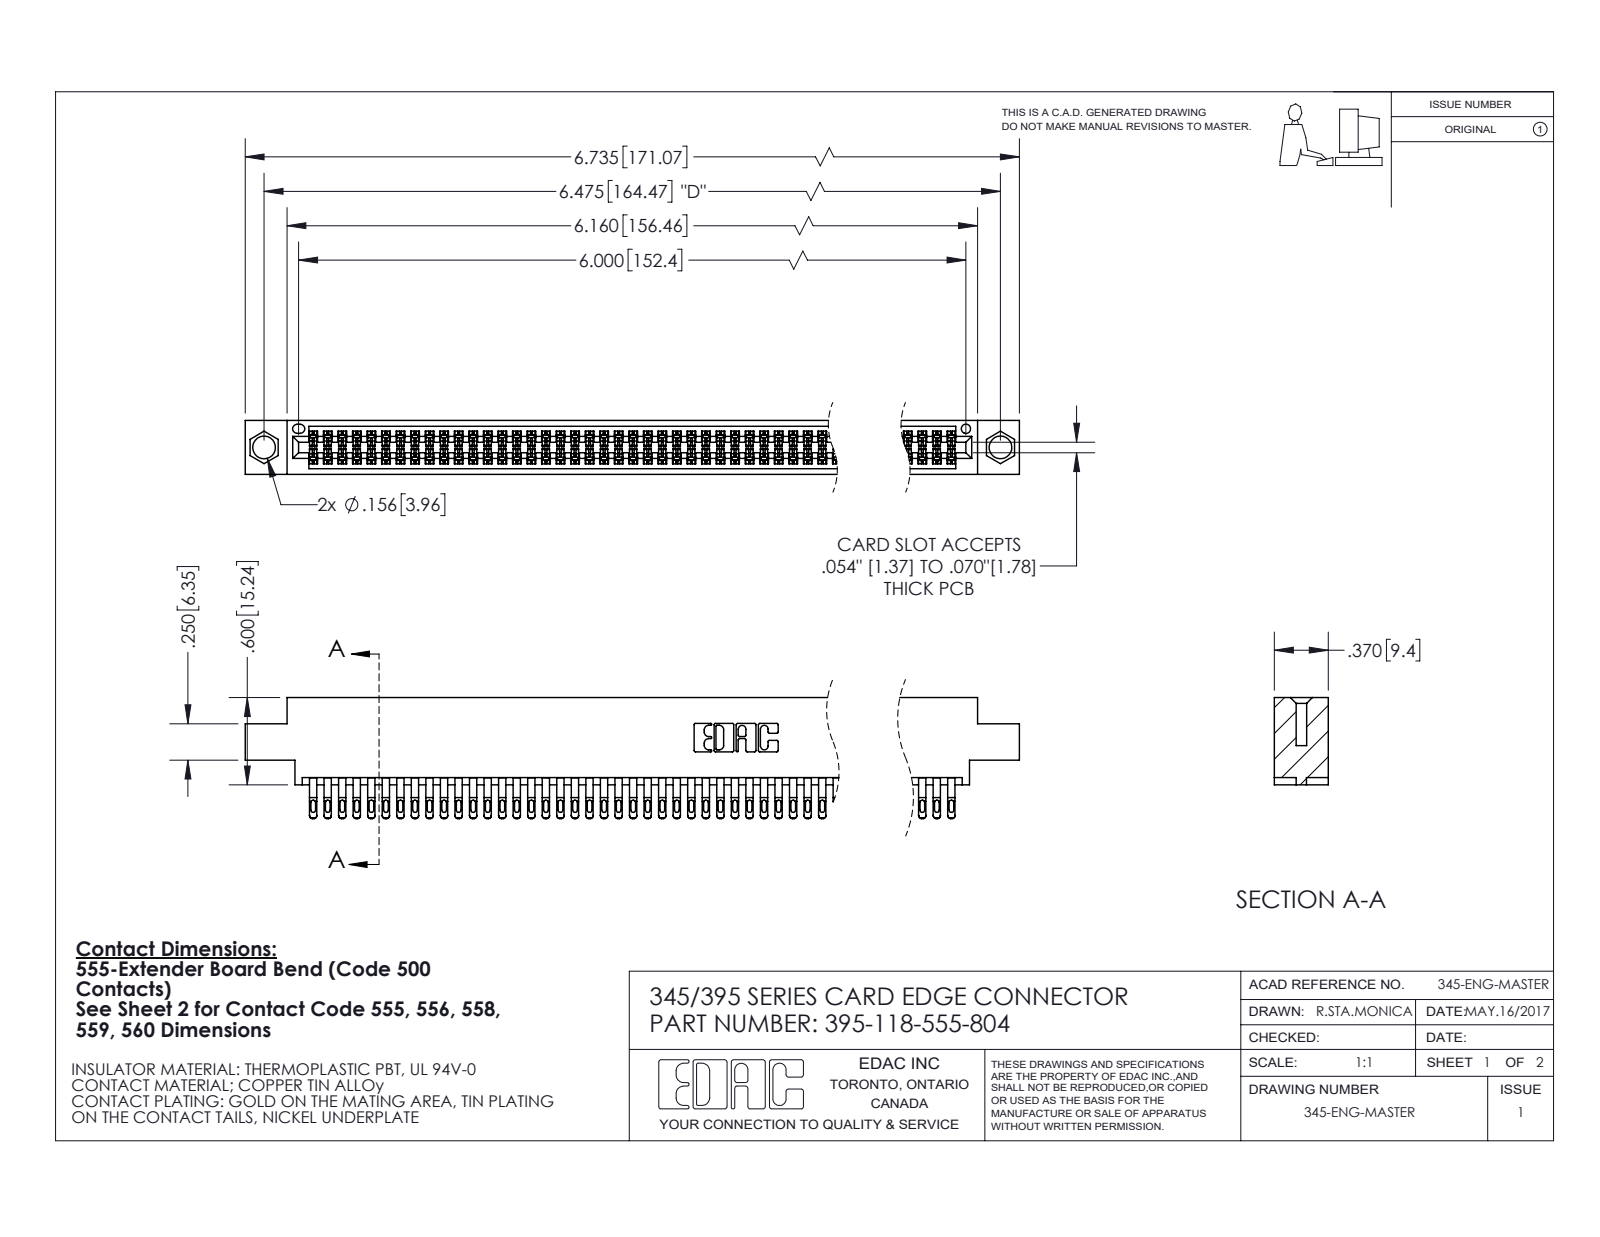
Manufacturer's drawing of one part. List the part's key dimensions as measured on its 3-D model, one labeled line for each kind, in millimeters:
Part name (STEP PRODUCT): 395-118-555-804; 345 Part_0.170 Offset - 0.156 Dia-TI; 345-292-001_555 Tail
STEP written by: SolidWorks 2020 (CONFIG_CONTROL_DESIGN)
Units: millimetres
Bodies: 119 solids, 6752 faces (3756 planar, 2996 cylindrical, 0 other)
Overall size (bounding box): 171.1 × 21.1 × 9.4
Volume: 16 900 mm³ · Surface area: 26 500 mm²
Round holes (diameter × count): ⌀4 ×2, ⌀1.6 ×1
Partial cylindrical surfaces — rounded edges, fillets, slot ends (radius × count): R0.4 ×295, R0.2 ×236, R0.5 ×236, R0.3 ×22, R0.2 ×6, R0.8 ×6, R0.7 ×3, R0.3 ×2
Main face-to-face distances: 1.8, 7.6, 0.6, 9.4, 5.1, 2.5, 6.9, 5.7, 4.4, 3.8
Hole centre spacings: 6.9, 158.5, 164.5
